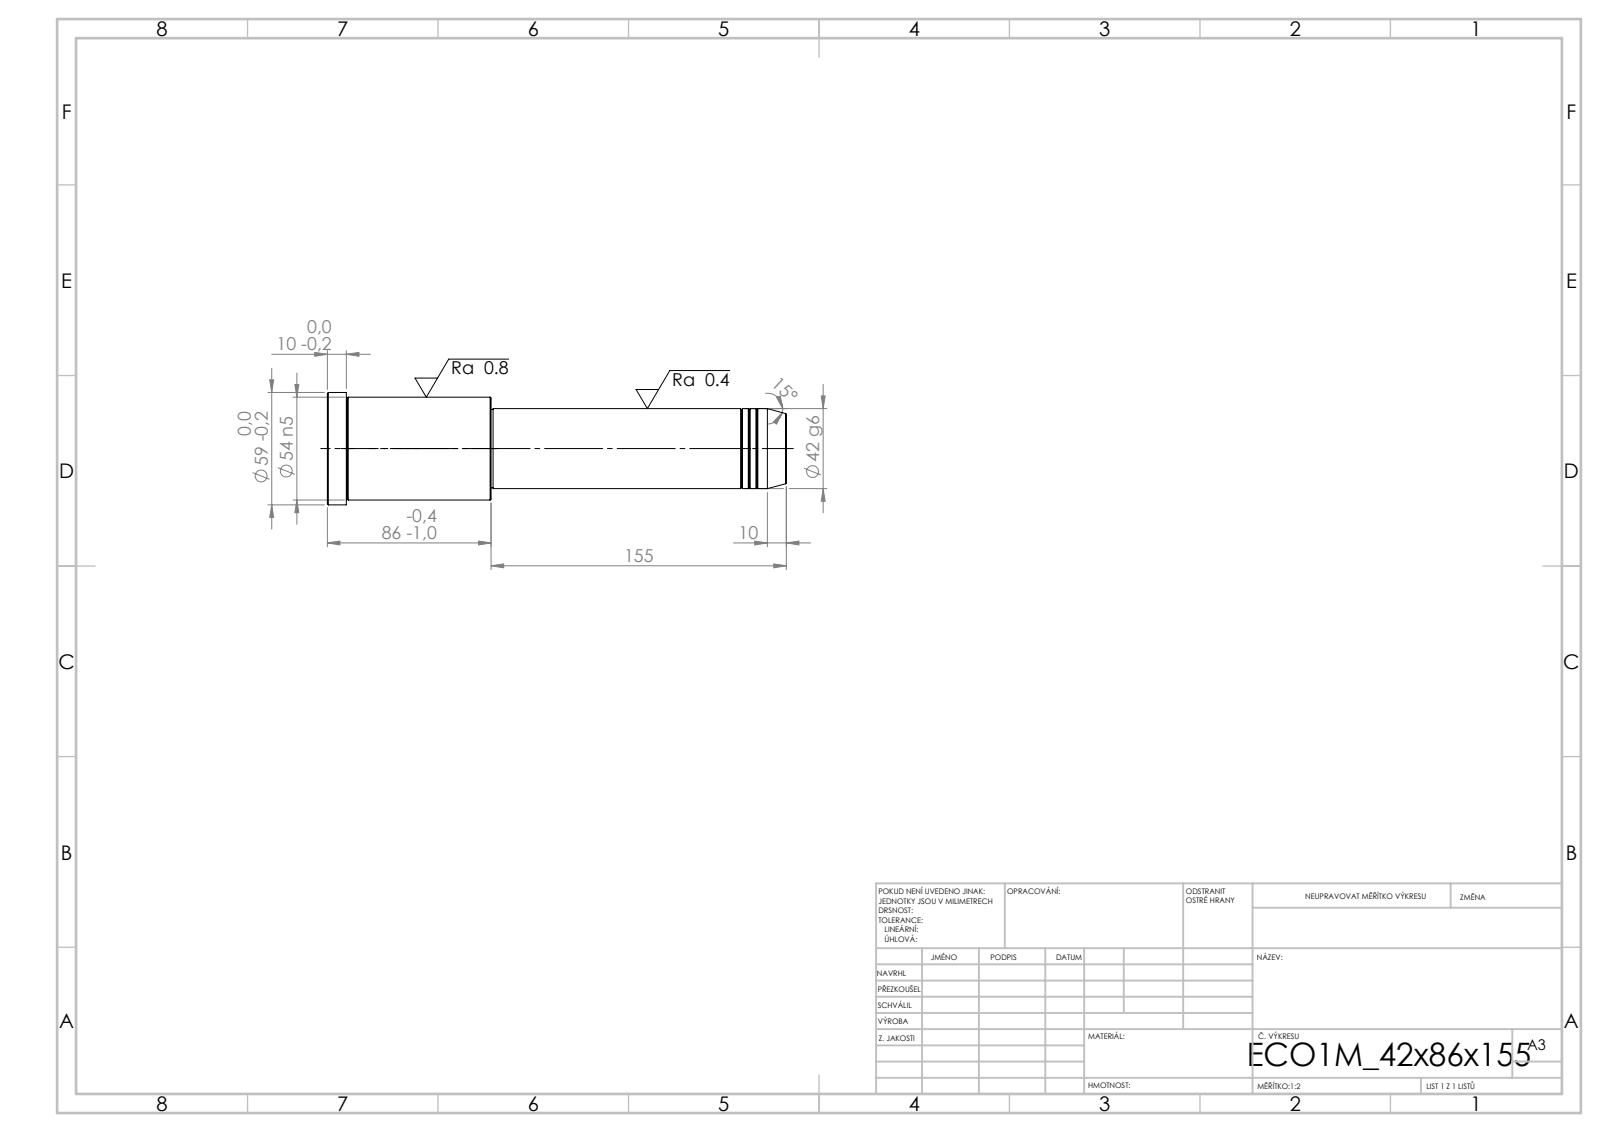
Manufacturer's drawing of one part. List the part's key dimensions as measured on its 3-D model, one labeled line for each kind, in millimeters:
STEP written by: SolidWorks 2019 (CONFIG_CONTROL_DESIGN)
Units: millimetres
Bodies: 1 solid, 43 faces (5 planar, 14 cylindrical, 24 other)
Overall size (bounding box): 241 × 59 × 59
Volume: 414 115 mm³ · Surface area: 40 615 mm²
Round bosses / shafts (diameter × count): ⌀59 ×1, ⌀54 ×1, ⌀42 ×1, ⌀41 ×1
Main face-to-face distances: 241, 155, 86, 231, 76, 10, 154, 1, 77, 87
